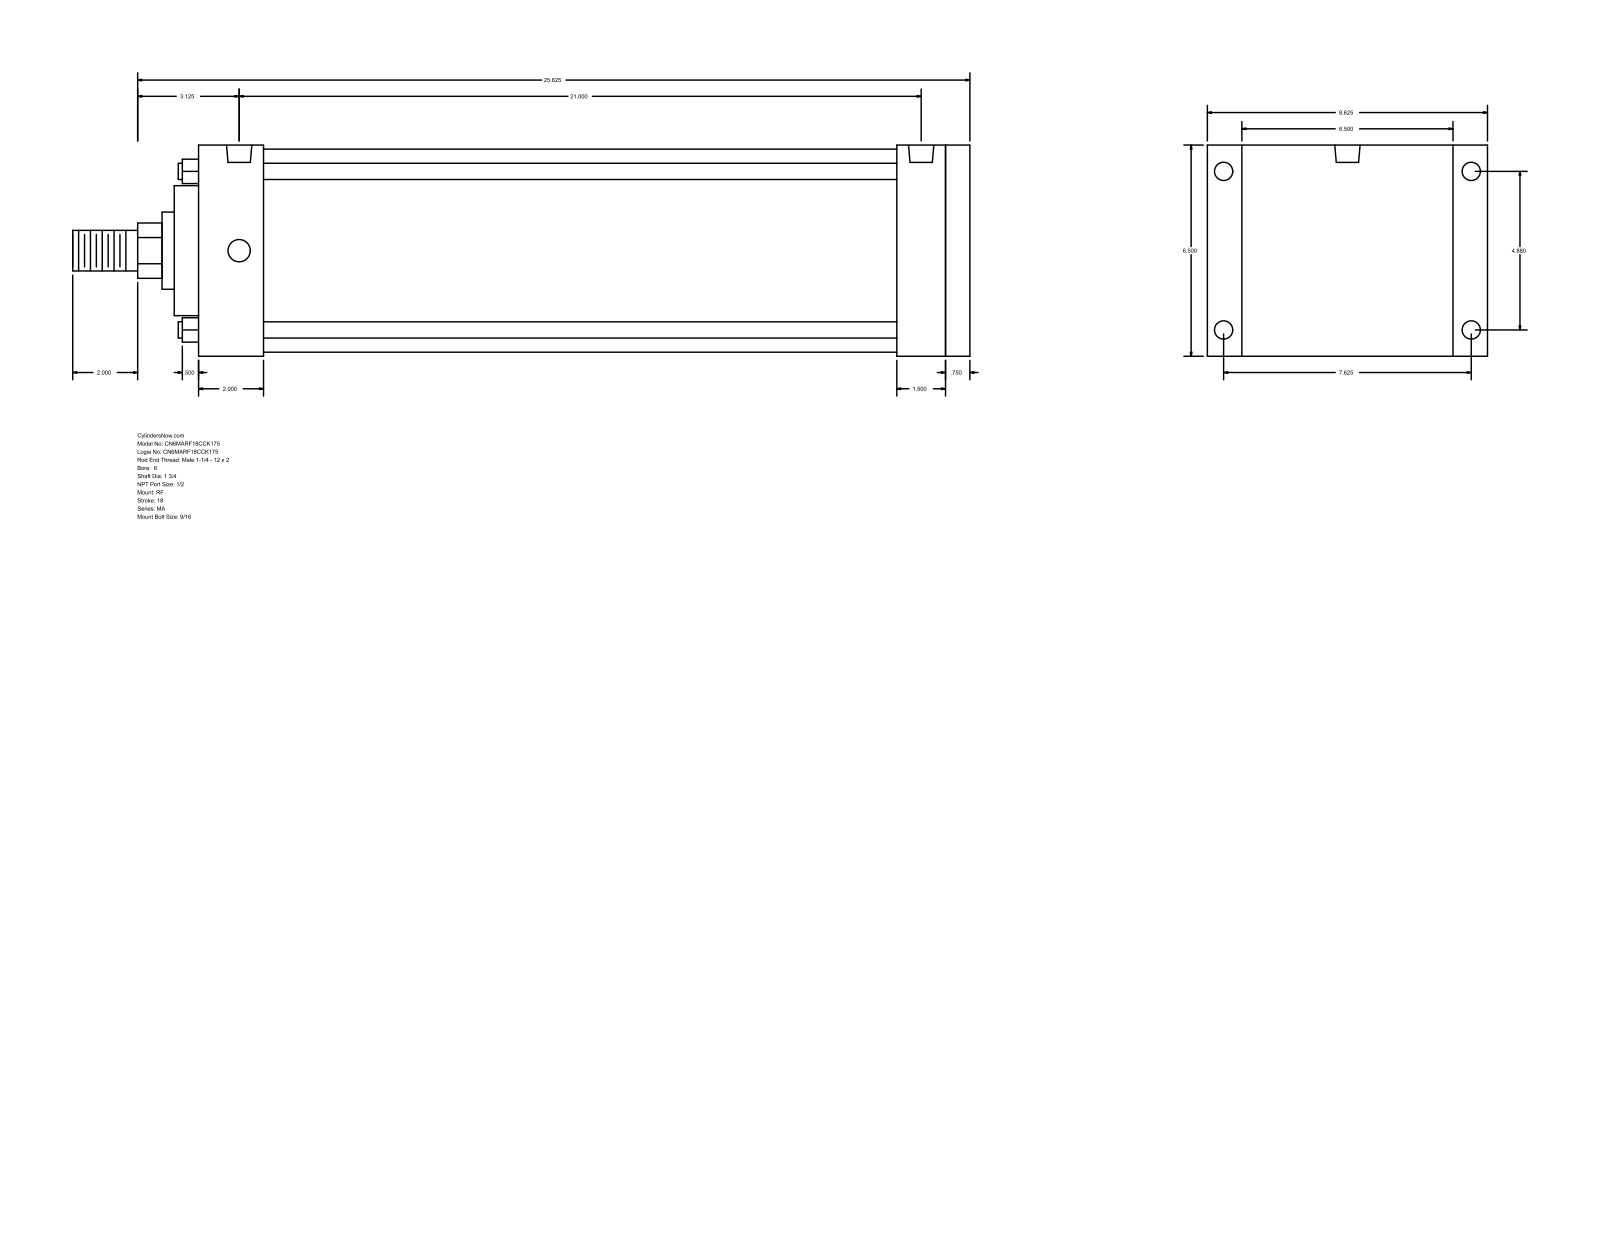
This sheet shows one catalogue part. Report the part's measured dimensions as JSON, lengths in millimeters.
{"part_name": "MA_RF__0600_1.75", "step_written_by": "GSSL Pune (CONFIG_CONTROL_DESIGN)", "units": "millimeters", "bodies": {"solids": 0, "faces": 94, "planar": 65, "cylindrical": 29, "other": 0}, "overall_size": [701.67, 219.07, 165.1], "round_holes": [[14.29, 4], [17.46, 4], [19.77, 2]], "round_bosses_or_shafts": [[12.7, 4], [158.75, 1], [101.6, 1], [60.33, 1], [44.45, 1], [31.75, 1]], "partial_cylinders_radius": [[21.63, 1]], "face_to_face_distances": [165.1, 603.26, 19.05, 584.21, 38.1, 50.8, 533.41, 552.46, 546.11, 495.31], "hole_center_spacings": [123.96, 193.68, 229.95, 533.39]}
